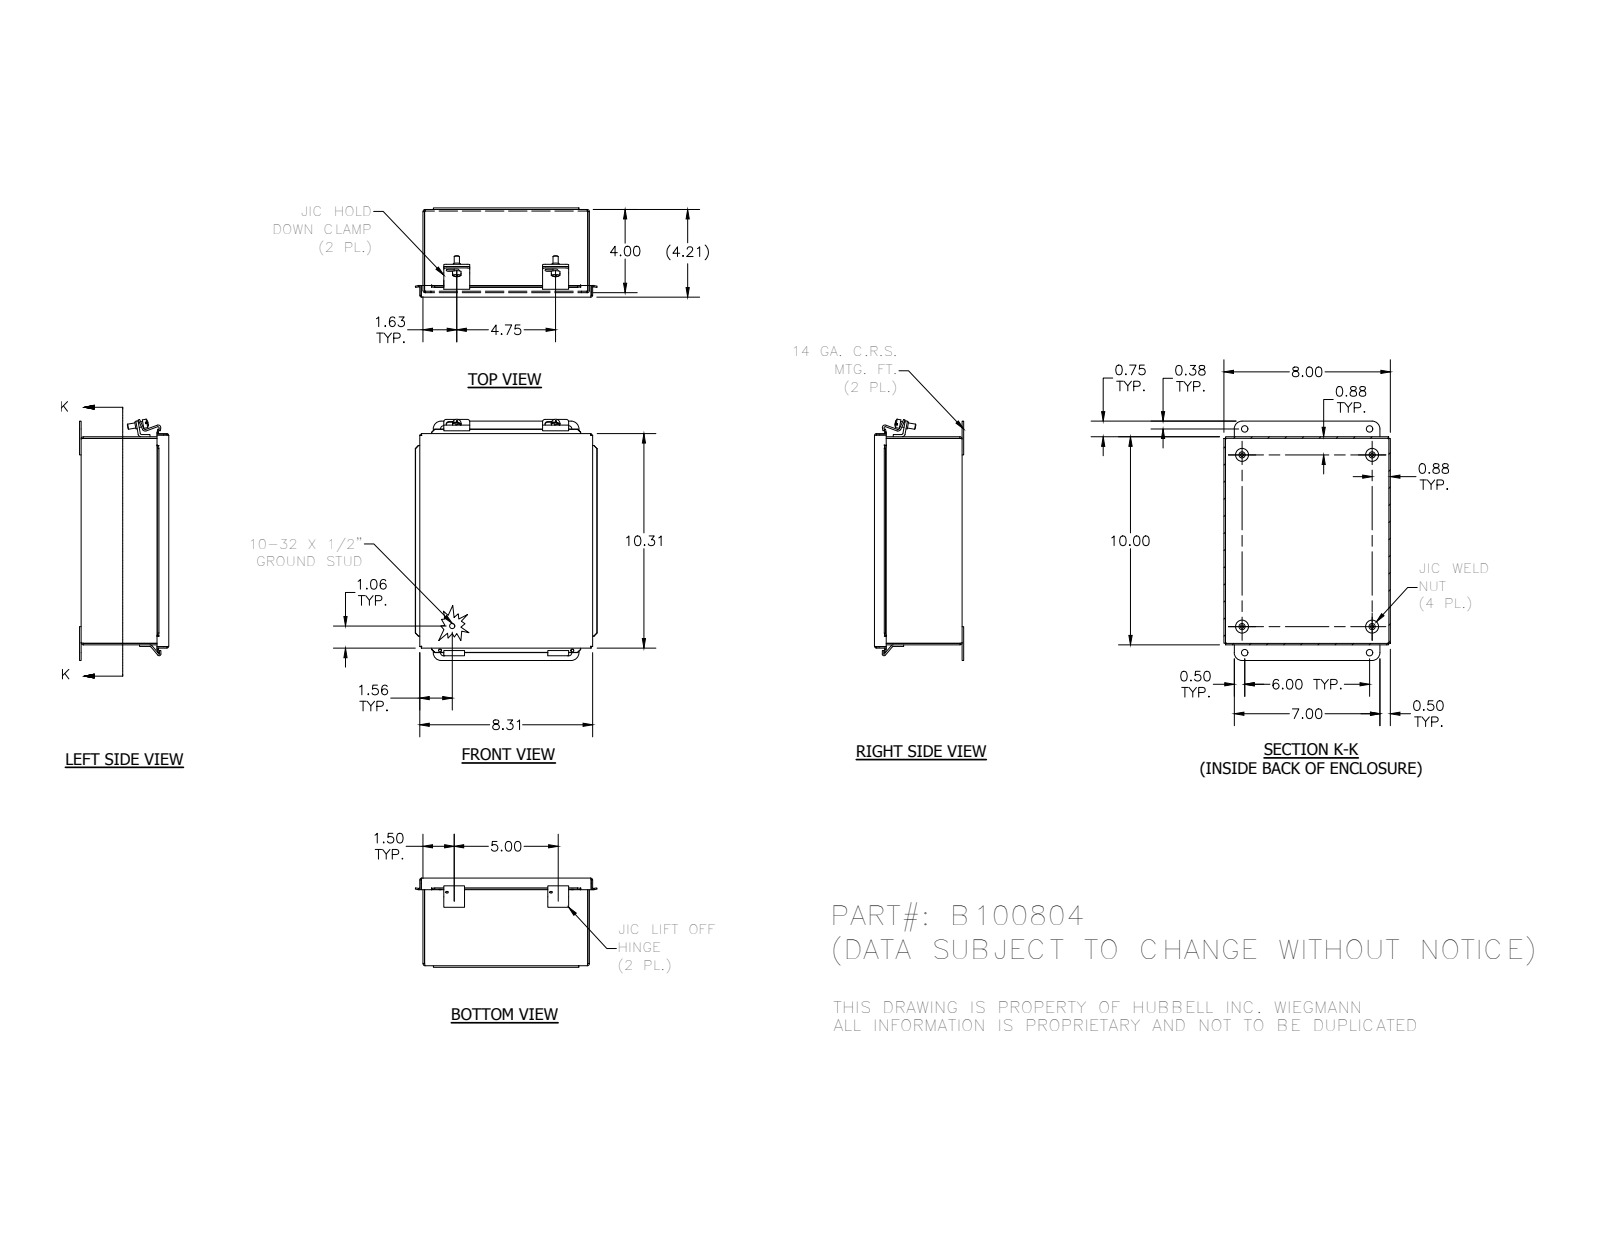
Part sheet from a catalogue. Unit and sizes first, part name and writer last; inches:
Units: inches
Overall size (bounding box): 11.593 × 8.739 × 4.287
Round holes (diameter × count): ⌀0.156 ×4, ⌀0.31 ×4, ⌀0.125 ×2, ⌀0.14 ×2, ⌀0.196 ×2
Round bosses / shafts (diameter × count): ⌀0.625 ×4, ⌀0.3 ×4, ⌀0.25 ×3, ⌀0.41 ×2, ⌀0.344 ×2, ⌀0.19 ×1
Partial cylindrical surfaces — rounded edges, fillets, slot ends (radius × count): R0.031 ×16, R0.093 ×8, R0.105 ×8, R0.125 ×8, R0.133 ×4, R0.375 ×4, R0.063 ×3, R0.126 ×3
Main face-to-face distances: 0.074, 4.15, 4.212, 0.062, 4.076, 4.138, 7.926, 9.926, 8, 7.852
Hole centre spacings: 1.256, 1.257, 6, 6.25, 6.251, 8.25, 9.5, 9.501
Volume: 30.39 in³ · Surface area: 813.4 in²
Bodies: 19 solids, 422 faces (279 planar, 98 cylindrical, 45 other)
Part name (STEP PRODUCT): B100804; 3499; 3483; C1001 (+7 more)
STEP written by: Autodesk Inventor 2012 (AUTOMOTIVE_DESIGN)
